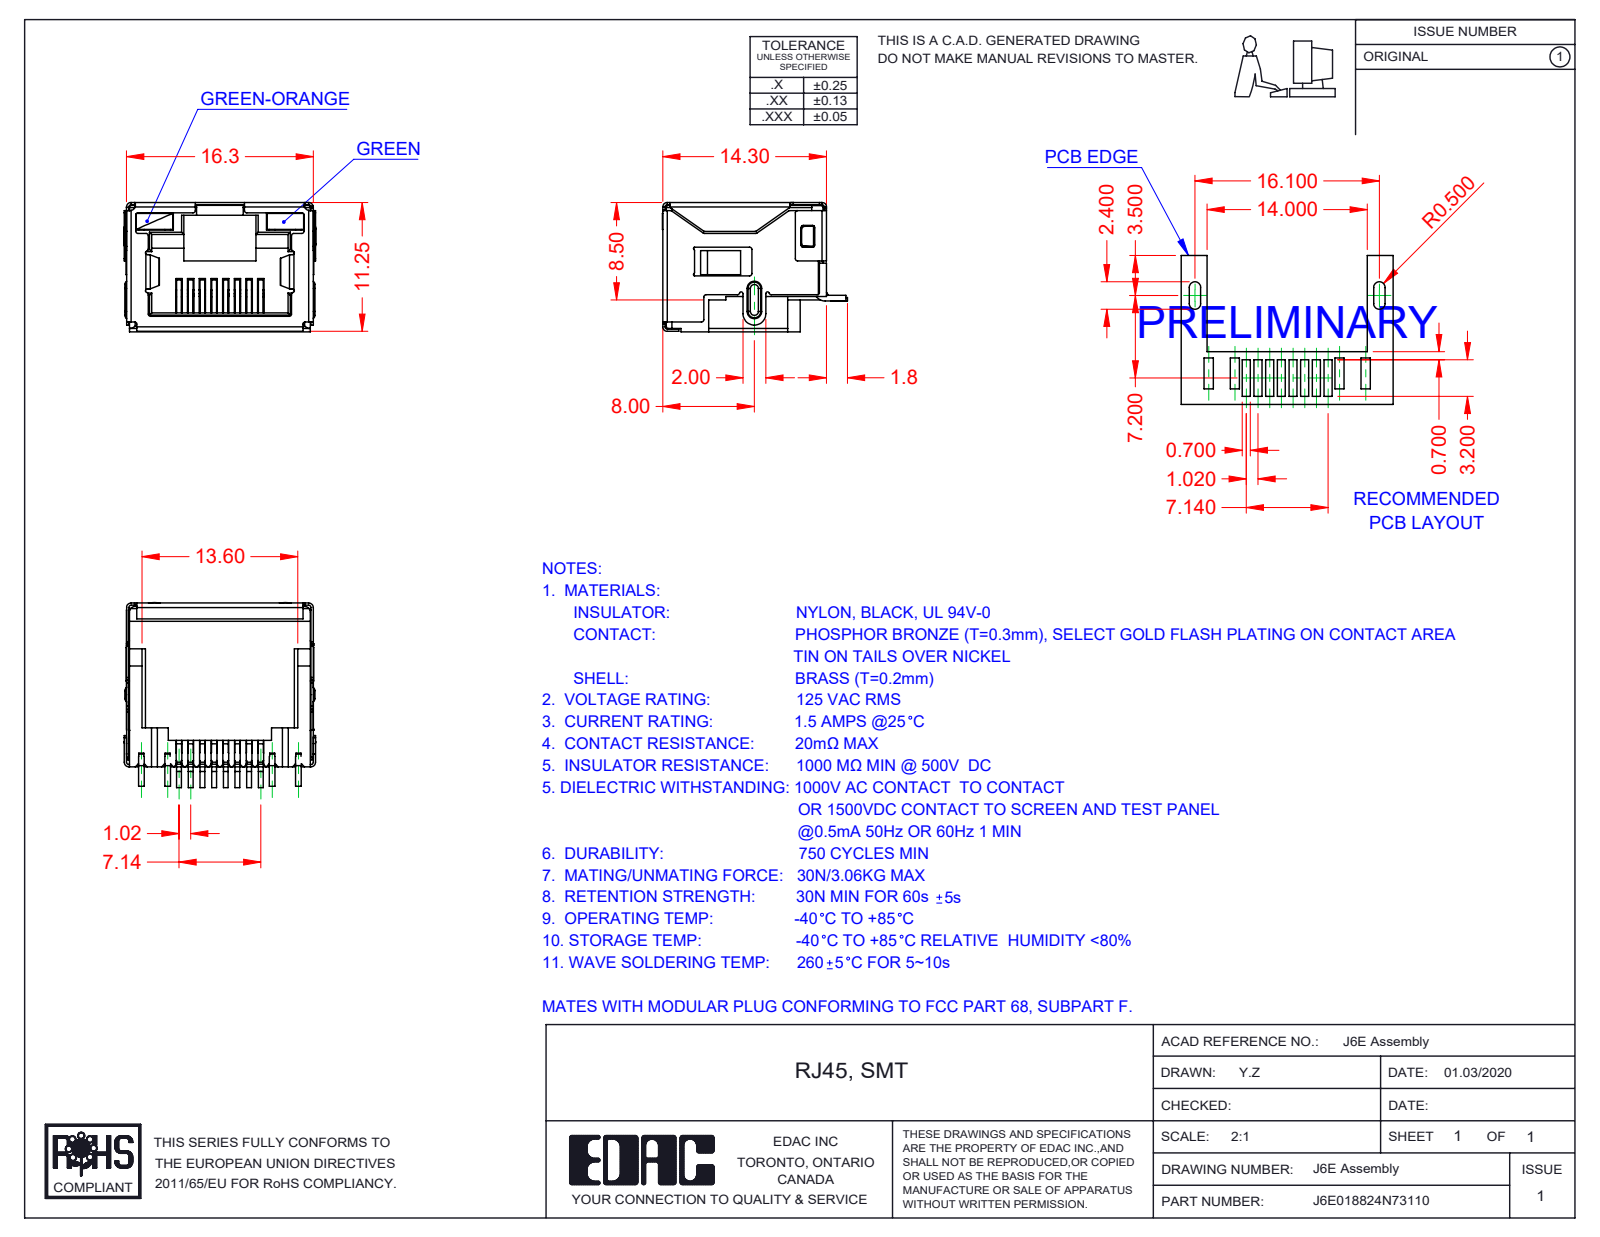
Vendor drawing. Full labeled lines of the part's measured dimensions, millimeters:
Part name (STEP PRODUCT): J6E018824N73110; 6E Insulator_LED; 6E Shield_LED; 6E LED LH_7-Green-Orange (+2 more)
STEP written by: SolidWorks 2016 (CONFIG_CONTROL_DESIGN)
Units: millimetres
Bodies: 12 solids, 1498 faces (1099 planar, 349 cylindrical, 50 other)
Overall size (bounding box): 16.75 × 16.15 × 11.3
Volume: 1 109 mm³ · Surface area: 4 045 mm²
Partial cylindrical surfaces — rounded edges, fillets, slot ends (radius × count): R0.2 ×82, R0.25 ×17, R0.4 ×13, R0.5 ×13, R0.1 ×10, R0.15 ×7, R0.3 ×4, R1 ×3
Main face-to-face distances: 11.05, 16.05, 16.1, 15.85, 11.1, 11.3, 2.4, 0.7, 9.85, 0.49
